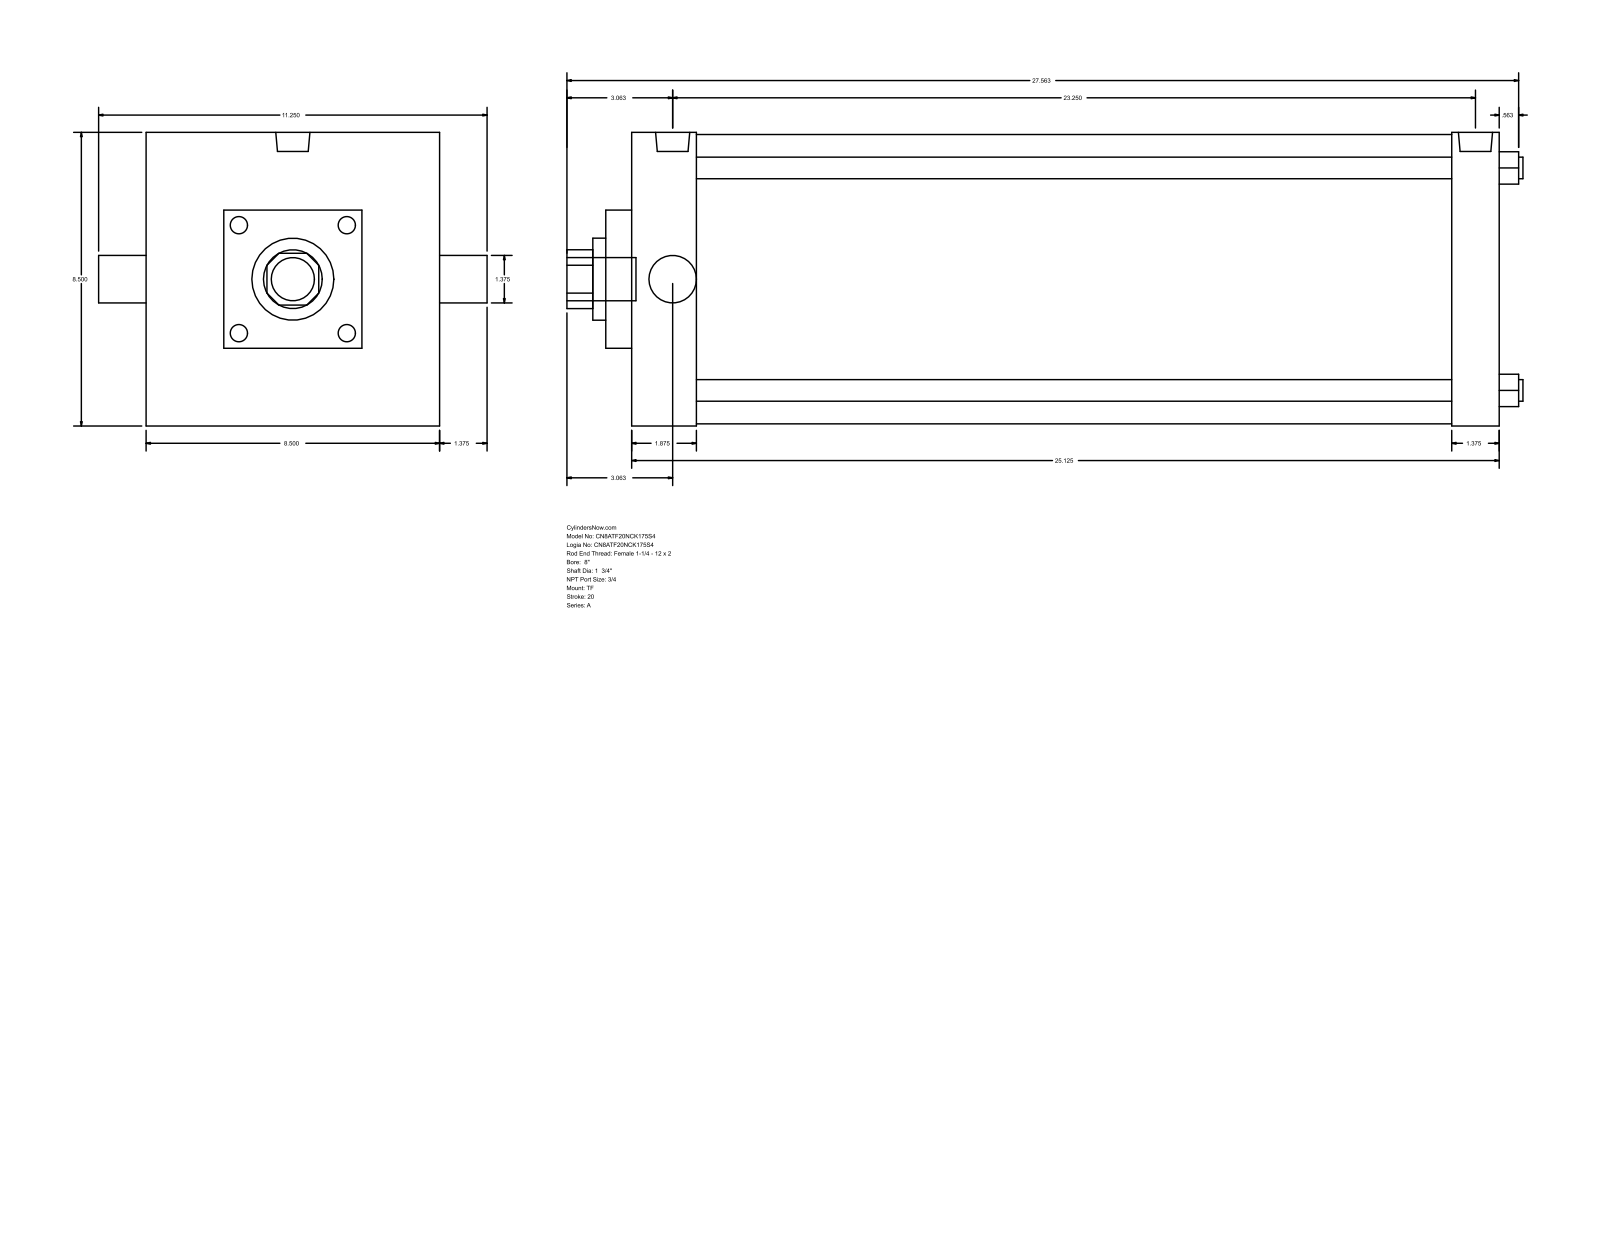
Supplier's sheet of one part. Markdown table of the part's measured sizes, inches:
| quantity | value |
| --- | --- |
| part name | A_TF__0800_1.75 |
| STEP written by | GSSL Pune (CONFIG_CONTROL_DESIGN) |
| units | inches |
| bodies | 0 solids, 89 faces (65 planar, 24 cylindrical, 0 other) |
| overall size | 27.687 × 11.25 × 8.5 |
| round holes (diameter × count) | 0.625 × 4, 1.375 × 1, 1.75 × 1, 2.375 × 1, 8.375 × 1 |
| round bosses / shafts (diameter × count) | 0.594 × 3, 0.989 × 2, 1.25 × 1 |
| partial cylindrical surfaces (radius × count) | 0.852 × 1 |
| main face-to-face distances | 25.125, 8.5, 1.375, 1.875, 23.25, 23.75, 21.875, 0.75, 2.25, 6.25 |
| hole center spacings | 4.554, 6.44, 9.108 |
